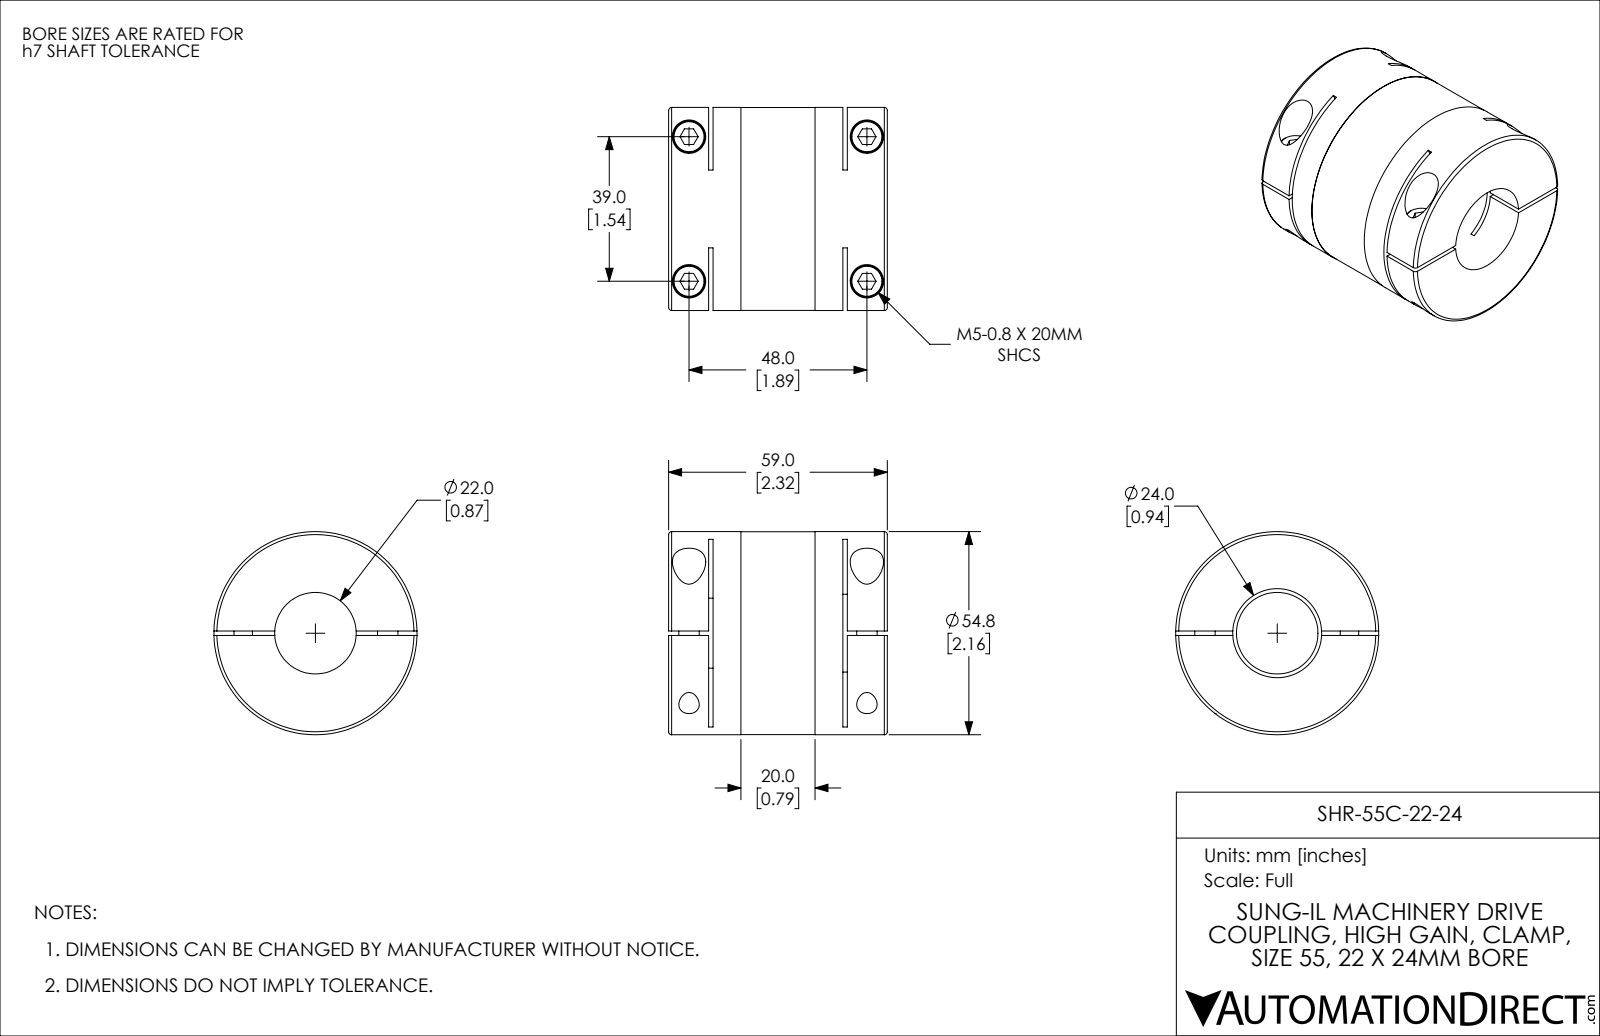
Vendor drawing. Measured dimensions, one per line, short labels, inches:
name: SHR-55C-22-24
written by: SolidWorks 2021 (CONFIG_CONTROL_DESIGN)
unit: in
bodies: 1 solid, 144 faces (70 planar, 58 cylindrical, 16 other)
size: 2.323 × 2.157 × 2.157
volume: 6.415 in³; area: 44.28 in²
holes: 4× ⌀0.217, 4× ⌀0.354, 1× ⌀0.866, 1× ⌀0.945, 1× ⌀1.024
bosses: 4× ⌀0.335, 2× ⌀0.197, 1× ⌀2.157, 1× ⌀2.154
rounds: 2× R2.362
face distances: 0.047, 0.472, 1.85, 0.425, 1.898, 1.425, 2.323, 1.378, 1.472, 0.768
hole spacings: 1.535, 1.89, 2.435
